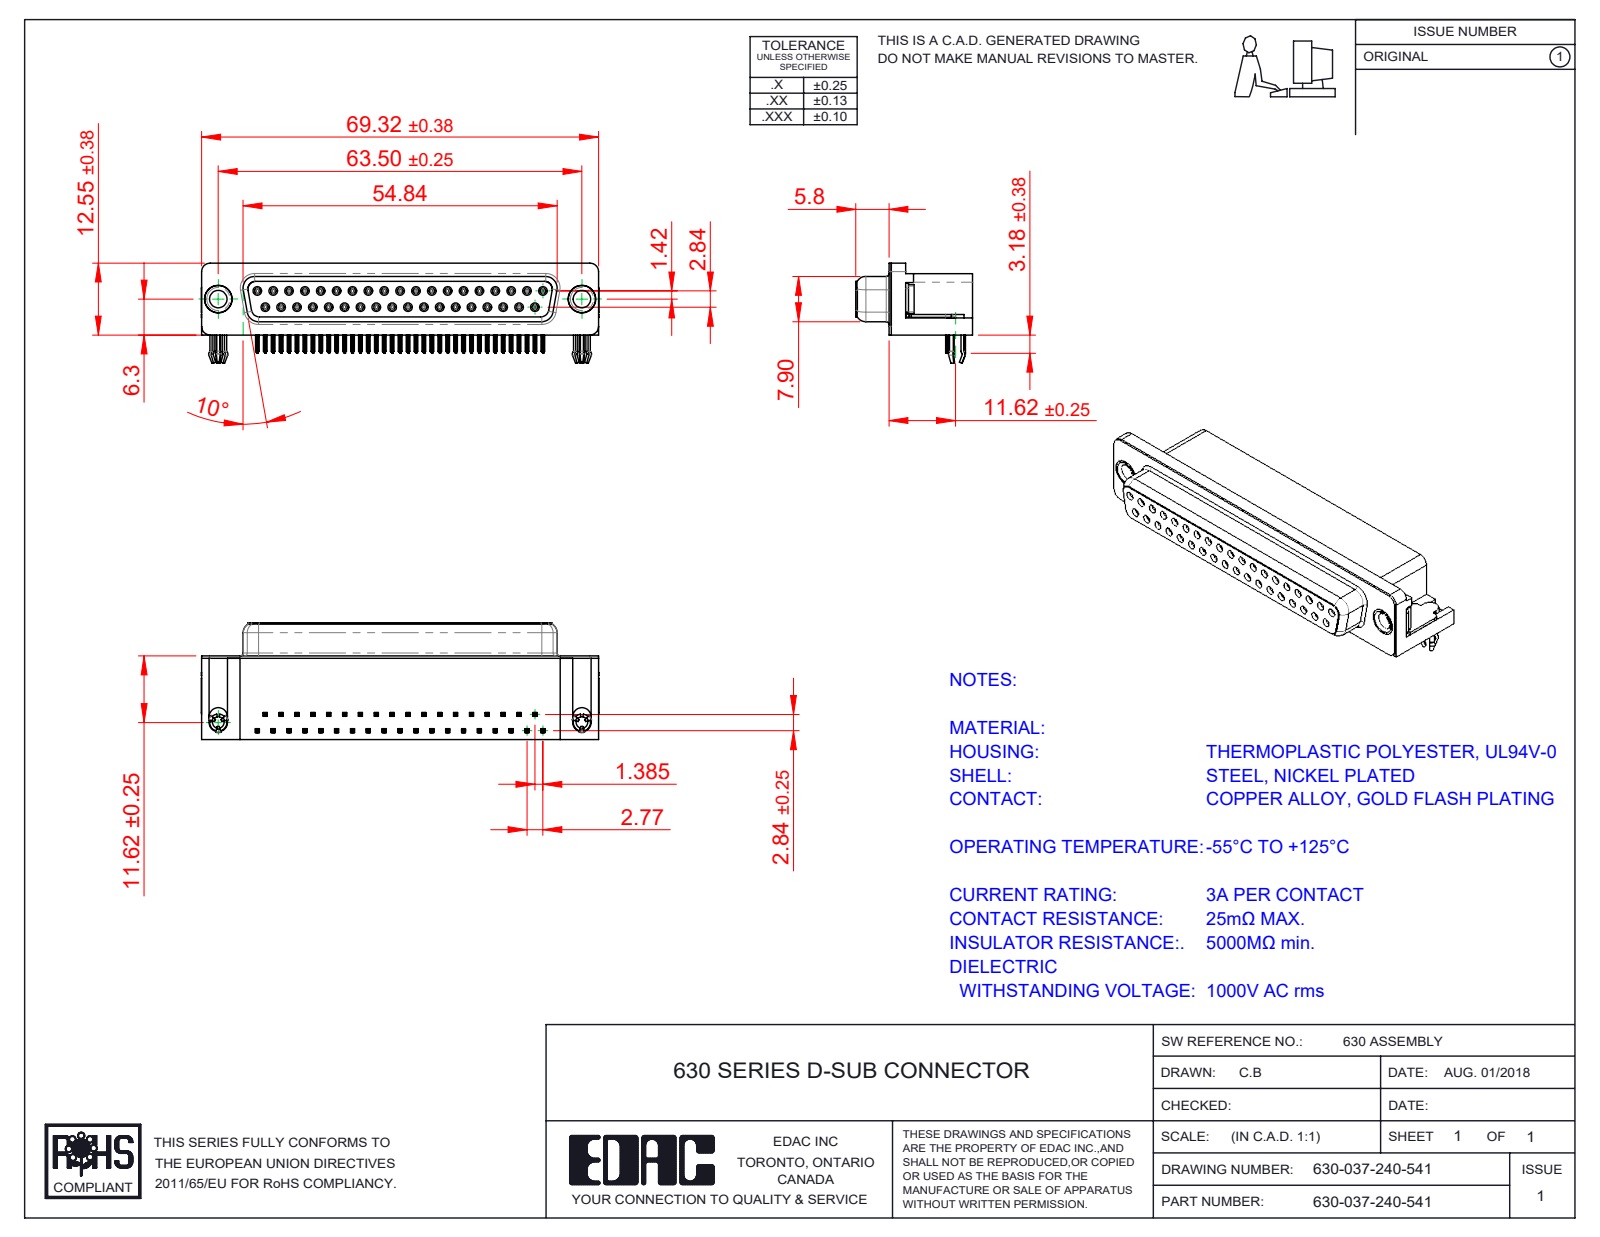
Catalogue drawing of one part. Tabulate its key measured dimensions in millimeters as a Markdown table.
| quantity | value |
| --- | --- |
| part name | 630 Contact Top; 630 Housing_37 Socket; 630-037-240-541; 630 Thru Hole Rivet (+3 more) |
| STEP written by | SolidWorks 2020 (CONFIG_CONTROL_DESIGN) |
| units | millimeters |
| bodies | 43 solids, 5624 faces (2540 planar, 1286 cylindrical, 1798 other) |
| overall size | 69.4 × 20.4 × 17.48 |
| volume | 11 815 mm³ |
| surface area | 13 603 mm² |
| round holes (diameter × count) | 0.8 × 37, 0.9 × 37, 2 × 2, 3.05 × 2, 4 × 2, 4.8 × 2, 5 × 2 |
| round bosses / shafts (diameter × count) | 1.2 × 37, 4.9 × 2, 4.75 × 2, 3.85 × 2, 3 × 2 |
| partial cylindrical surfaces (radius × count) | 0.1 × 296, 0.15 × 148, 0.35 × 74, 0.34 × 37, 0.28 × 18, 1 × 18, 0.25 × 12, 1.35 × 8 |
| main face-to-face distances | 0.4, 6.2, 10.34, 14.2, 2.84, 0.85, 6.65, 0.45, 14.6, 2.9 |
| hole center spacings | 3.16, 2.77, 5.54, 8.31, 11.08, 13.85, 16.62, 19.39 |
